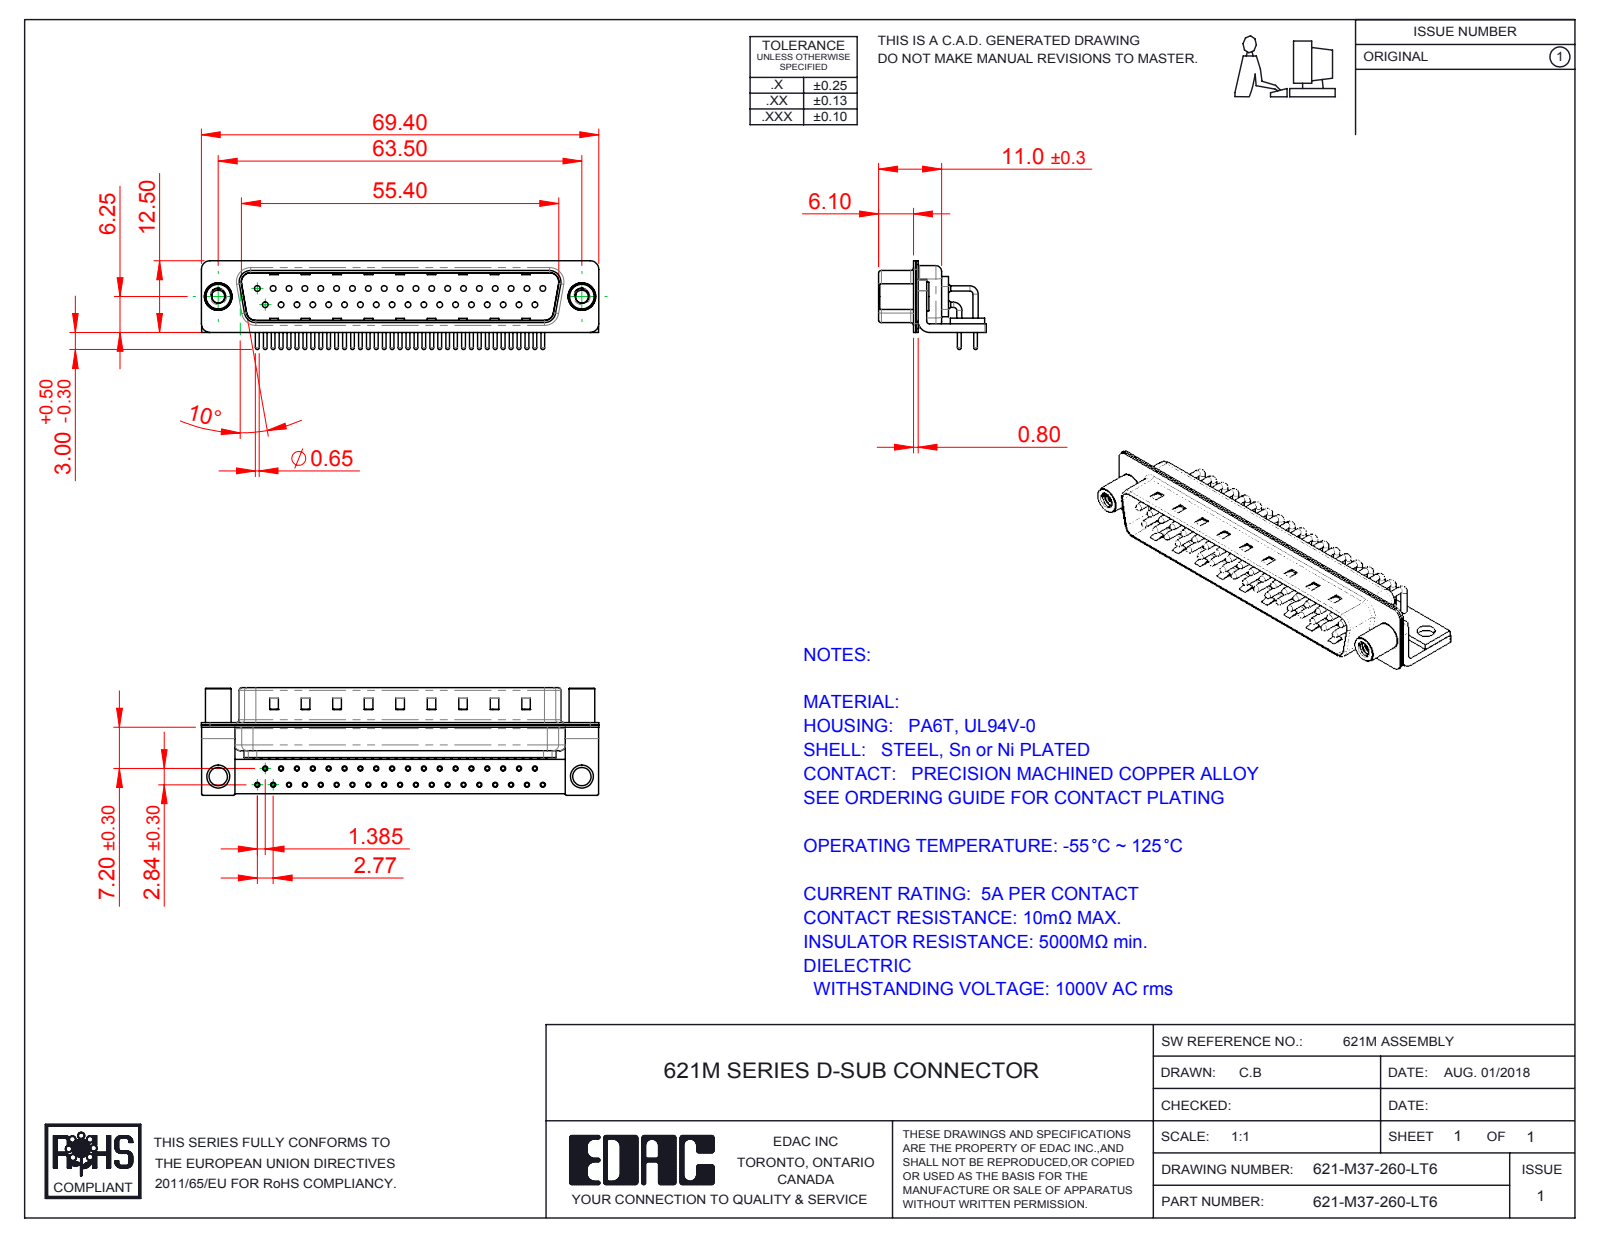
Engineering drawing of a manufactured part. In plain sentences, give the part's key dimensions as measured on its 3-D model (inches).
The part is named "621M Shell Front_37 Contacts; 621M Contact Row 2; 621M Shell Rear_37 Contacts; 621-M37-260-LT6 (+5 more)". Its 3-D file was written by "SolidWorks 2016 (CONFIG_CONTROL_DESIGN)". It is 45 solids with 4656 faces: 2599 planar, 1611 cylindrical and 446 other. Overall it measures 2.732 by 0.74 by 0.61 inches. Its volume is 0.288 cubic inches and its surface area 18.96 square inches. Round holes: 37 of diameter 0.035, 37 of diameter 0.039, 37 of diameter 0.067, 37 of diameter 0.079, 2 of diameter 0.089, 2 of diameter 0.126, 2 of diameter 0.157, 2 of diameter 0.189. Round bosses or shafts: 46 of diameter 0.035, 37 of diameter 0.059, 37 of diameter 0.026, 2 of diameter 0.197, 2 of diameter 0.193, 2 of diameter 0.177. Partial cylindrical surfaces (rounded edges, fillets, slot ends): 37 of radius 0.04, 16 of radius 0.01, 16 of radius 0.059, 13 of radius 0.079, 9 of radius 0.02, 8 of radius 0.063, 4 of radius 0.024, 4 of radius 0.026. The main face-to-face distances are 0.016, 0.033, 0.049, 0.376, 0.059, 0.327, 0.031, 0.409, 0.343, 0.039. The hole center spacings are 0.124, 0.109, 0.218, 0.327, 0.436, 0.545, 0.198, 0.654.
